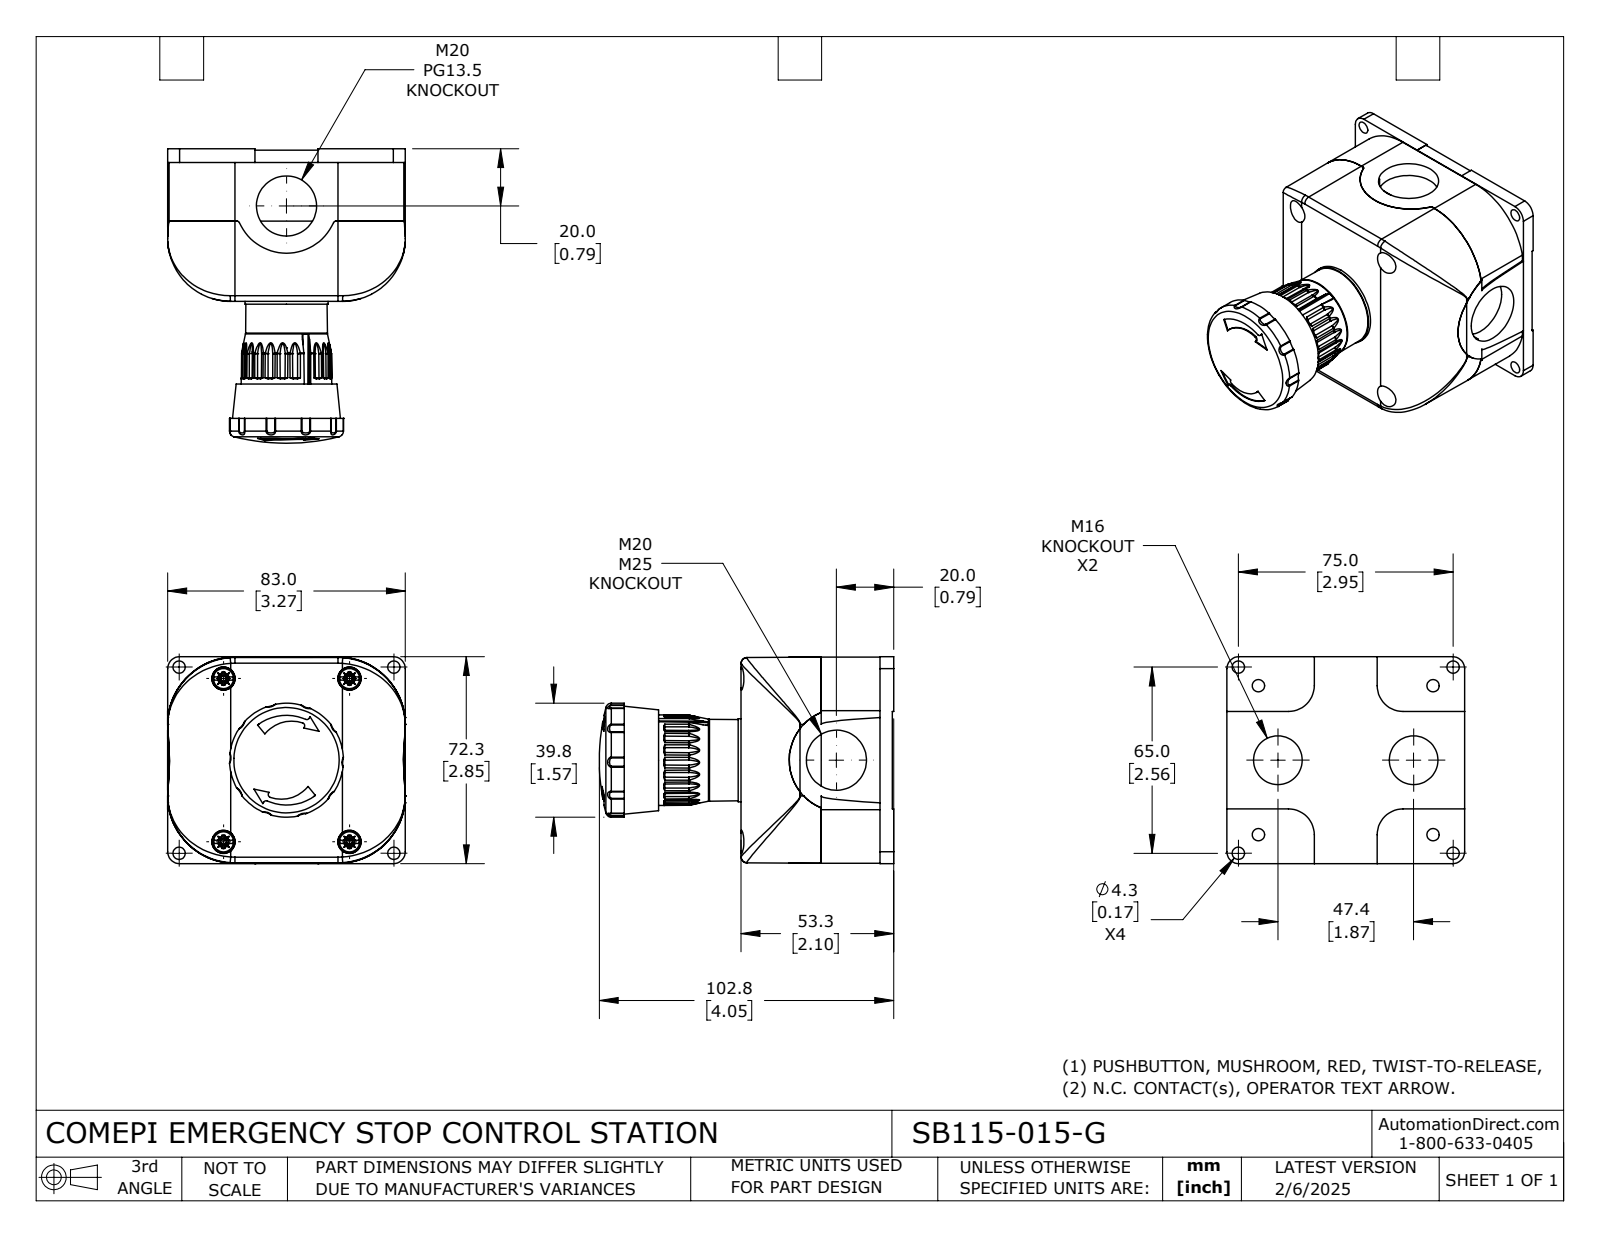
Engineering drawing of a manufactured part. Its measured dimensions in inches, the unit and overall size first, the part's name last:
Units: inches
Overall size (bounding box): 4.048 × 3.268 × 2.846
Round holes (diameter × count): ⌀0.169 ×8, ⌀0.323 ×4, ⌀0.669 ×2, ⌀0.827 ×2, ⌀0.051 ×1, ⌀0.713 ×1, ⌀0.854 ×1
Round bosses / shafts (diameter × count): ⌀0.276 ×4, ⌀1.142 ×1, ⌀0.925 ×1, ⌀0.874 ×1, ⌀0.843 ×1
Partial cylindrical surfaces — rounded edges, fillets, slot ends (radius × count): R0.039 ×28, R0.268 ×10, R0.035 ×4, R0.079 ×4, R0.354 ×4, R0.38 ×4, R0.925 ×4, R0.01 ×2
Main face-to-face distances: 0.976, 0.098, 0.878, 2.079, 1.98, 1.102, 0.118, 0.02, 0.996, 2.098
Hole centre spacings: 0.376, 1.058, 1.39, 1.578, 1.954, 2.32, 2.367, 2.689
Volume: 14.31 in³ · Surface area: 106.3 in²
Bodies: 5 solids, 901 faces (353 planar, 192 cylindrical, 356 other)
Part name (STEP PRODUCT): SB115-015-G
STEP written by: SolidWorks 2024 (CONFIG_CONTROL_DESIGN)
